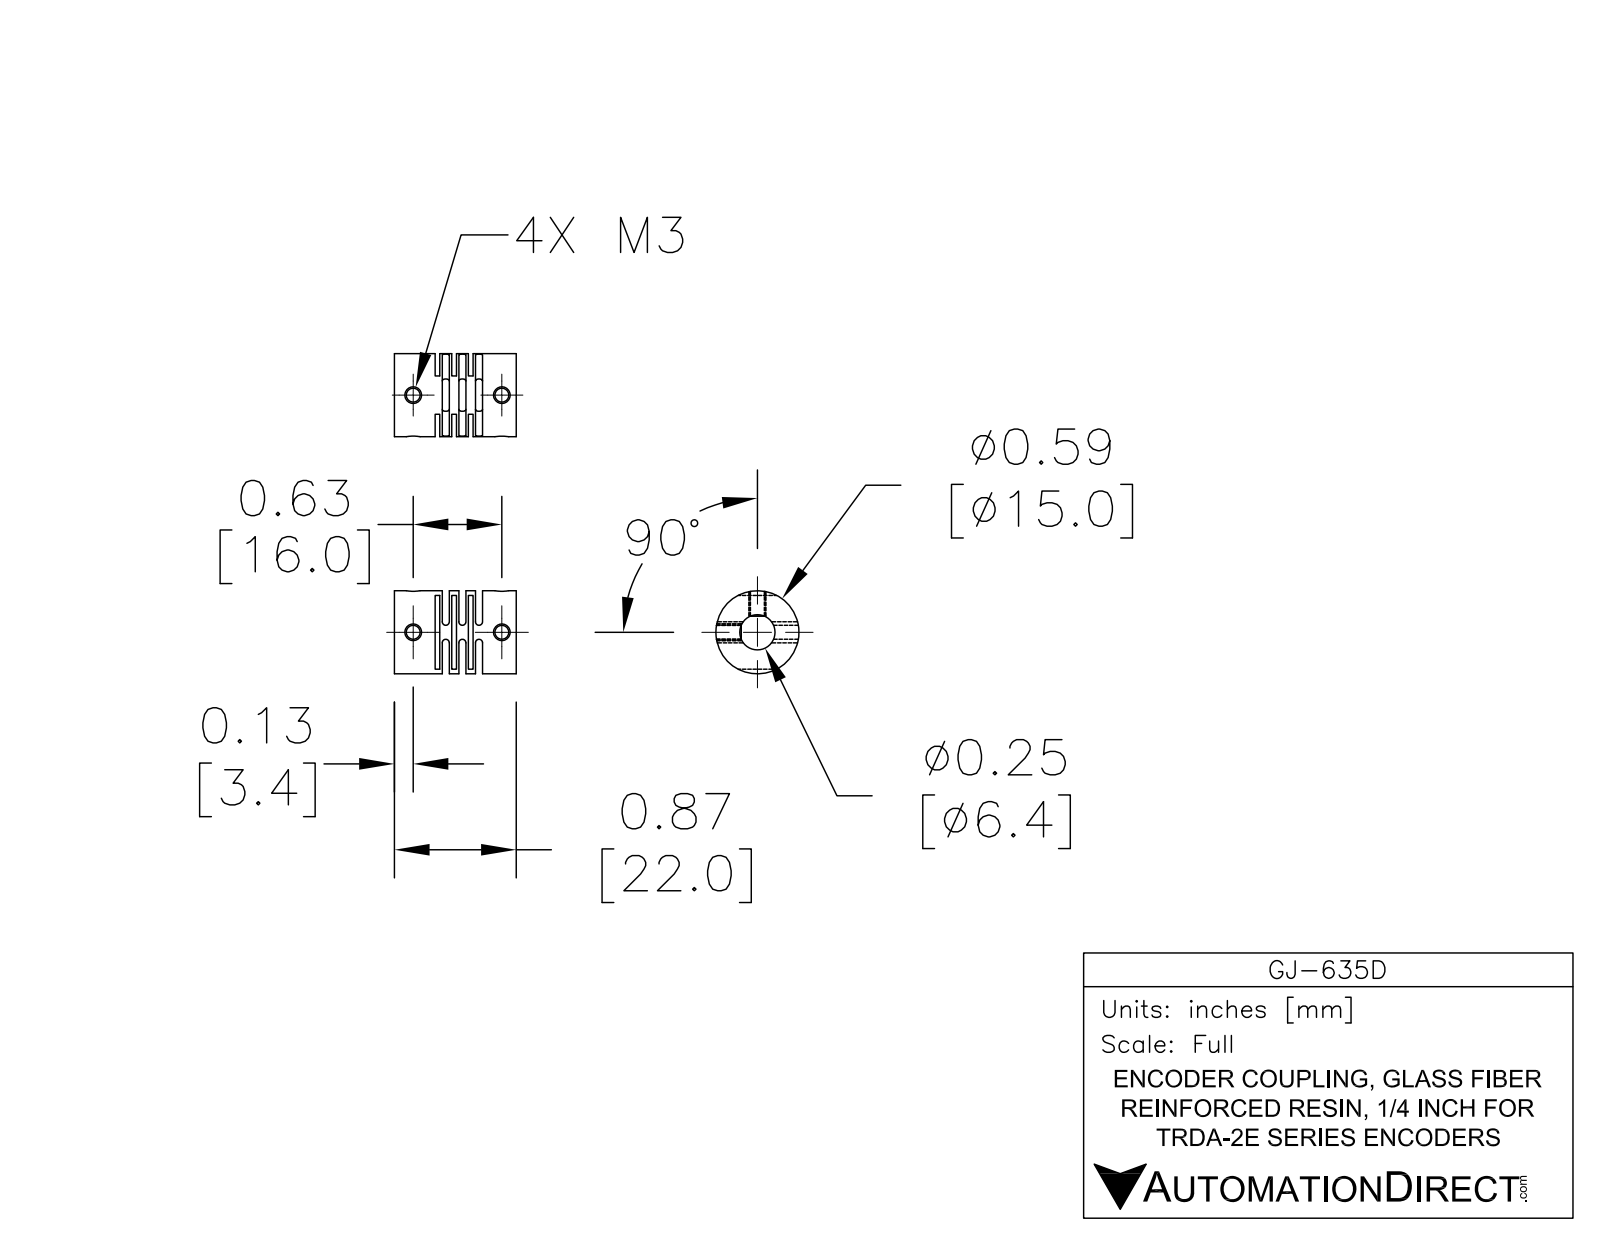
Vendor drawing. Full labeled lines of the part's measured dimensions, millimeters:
Part name (STEP PRODUCT): GJ-635D
STEP written by: SolidWorks 2016 (AUTOMOTIVE_DESIGN)
Units: millimetres
Bodies: 1 solid, 146 faces (94 planar, 20 cylindrical, 32 other)
Overall size (bounding box): 22 × 15 × 15
Volume: 2 381 mm³ · Surface area: 2 894 mm²
Round holes (diameter × count): ⌀2.5 ×4, ⌀6.35 ×1
Round bosses / shafts (diameter × count): ⌀15 ×1
Main face-to-face distances: 5.2, 2.6, 7.8, 1.2, 6.4, 9, 10.4, 3.8, 1.4, 4
Hole centre spacings: 16
